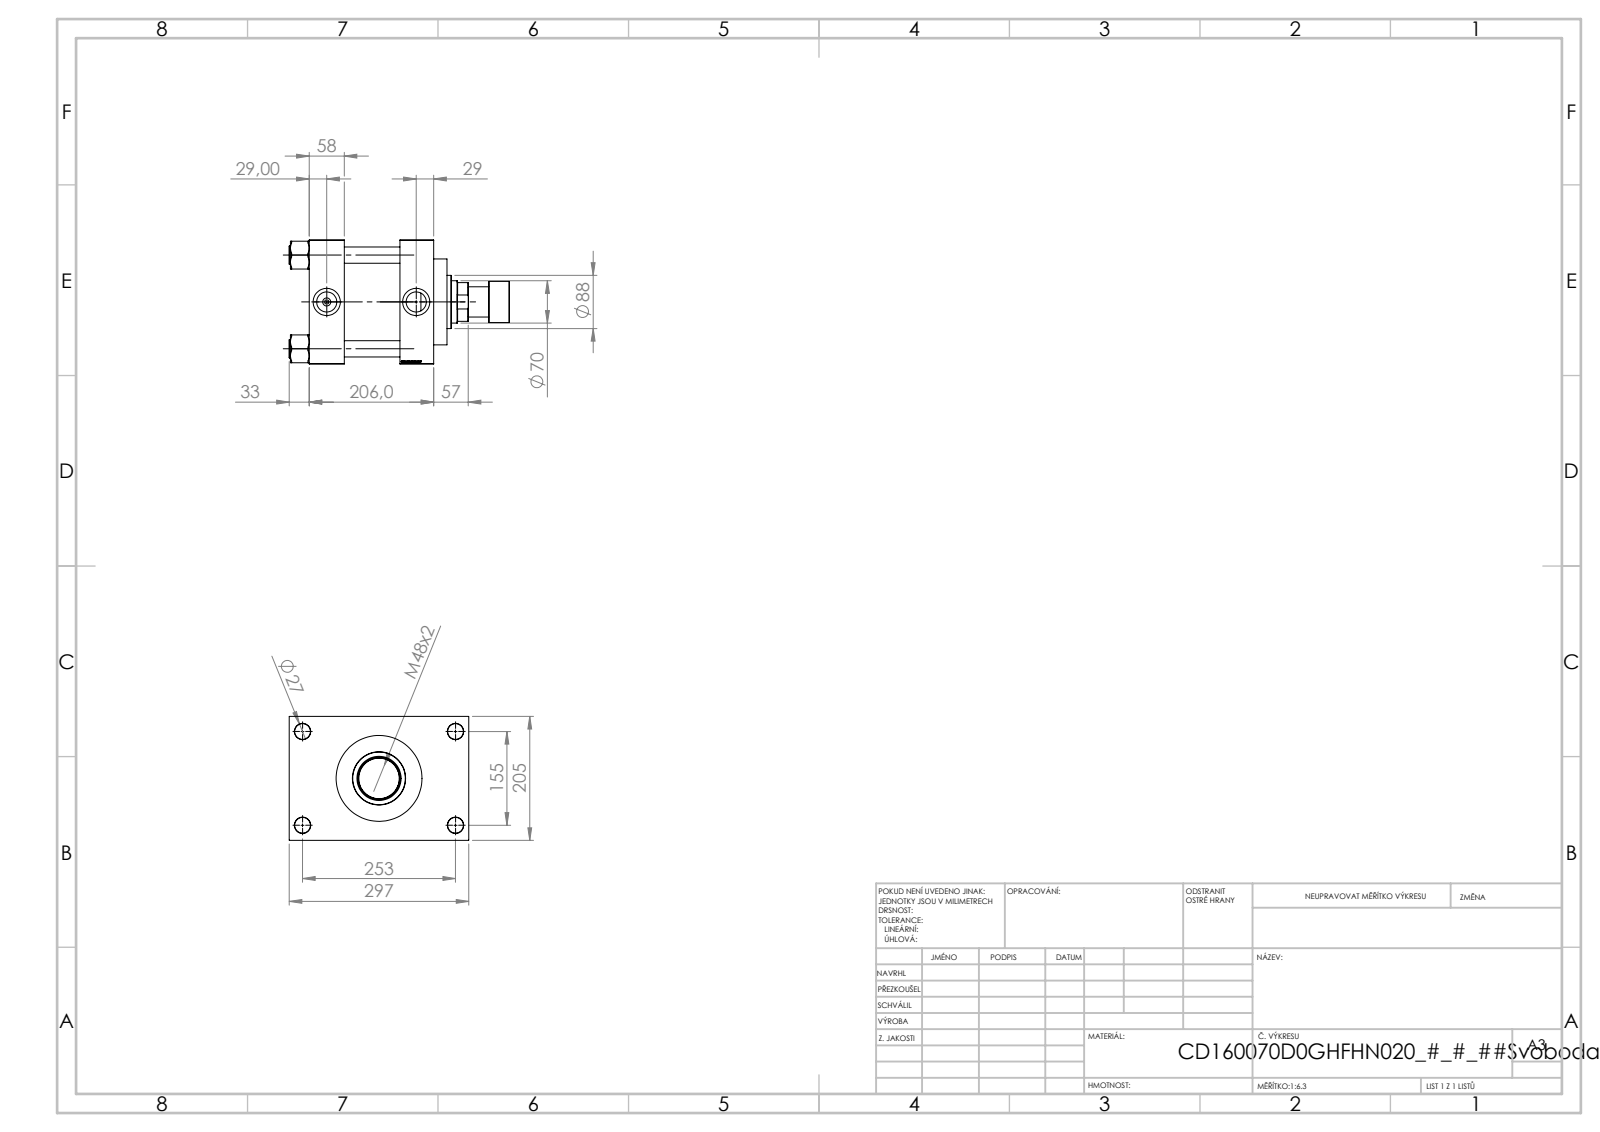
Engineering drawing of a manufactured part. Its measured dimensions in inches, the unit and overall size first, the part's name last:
Units: inches
Overall size (bounding box): 14.331 × 11.693 × 8.071
Round holes (diameter × count): ⌀1.024 ×4, ⌀1.063 ×4, ⌀0.276 ×2, ⌀1.309 ×2, ⌀1.772 ×2, ⌀1.831 ×1, ⌀2.756 ×1, ⌀2.874 ×1, ⌀4.724 ×1, ⌀5.591 ×1, ⌀6.299 ×1
Round bosses / shafts (diameter × count): ⌀1.181 ×4, ⌀6.535 ×1, ⌀3.465 ×1, ⌀2.677 ×1, ⌀1.969 ×1, ⌀1.929 ×1
Main face-to-face distances: 2.283, 5.906, 3.622, 8.11, 5.827, 2.205, 8.071, 1.811, 9.882, 2.835
Hole centre spacings: 1.931, 4.312, 5.841, 6.098, 6.399, 8.03, 10.084, 6.102
Volume: 491 in³ · Surface area: 1 162 in²
Bodies: 12 solids, 1162 faces (548 planar, 92 cylindrical, 522 other)
Part name (STEP PRODUCT): V215CR_ROD_END_F; V215CD_D_Body; V215CD_NUT_M5_D; V215CD_VC_A (+2 more)
STEP written by: SolidWorks 2019 (CONFIG_CONTROL_DESIGN)
